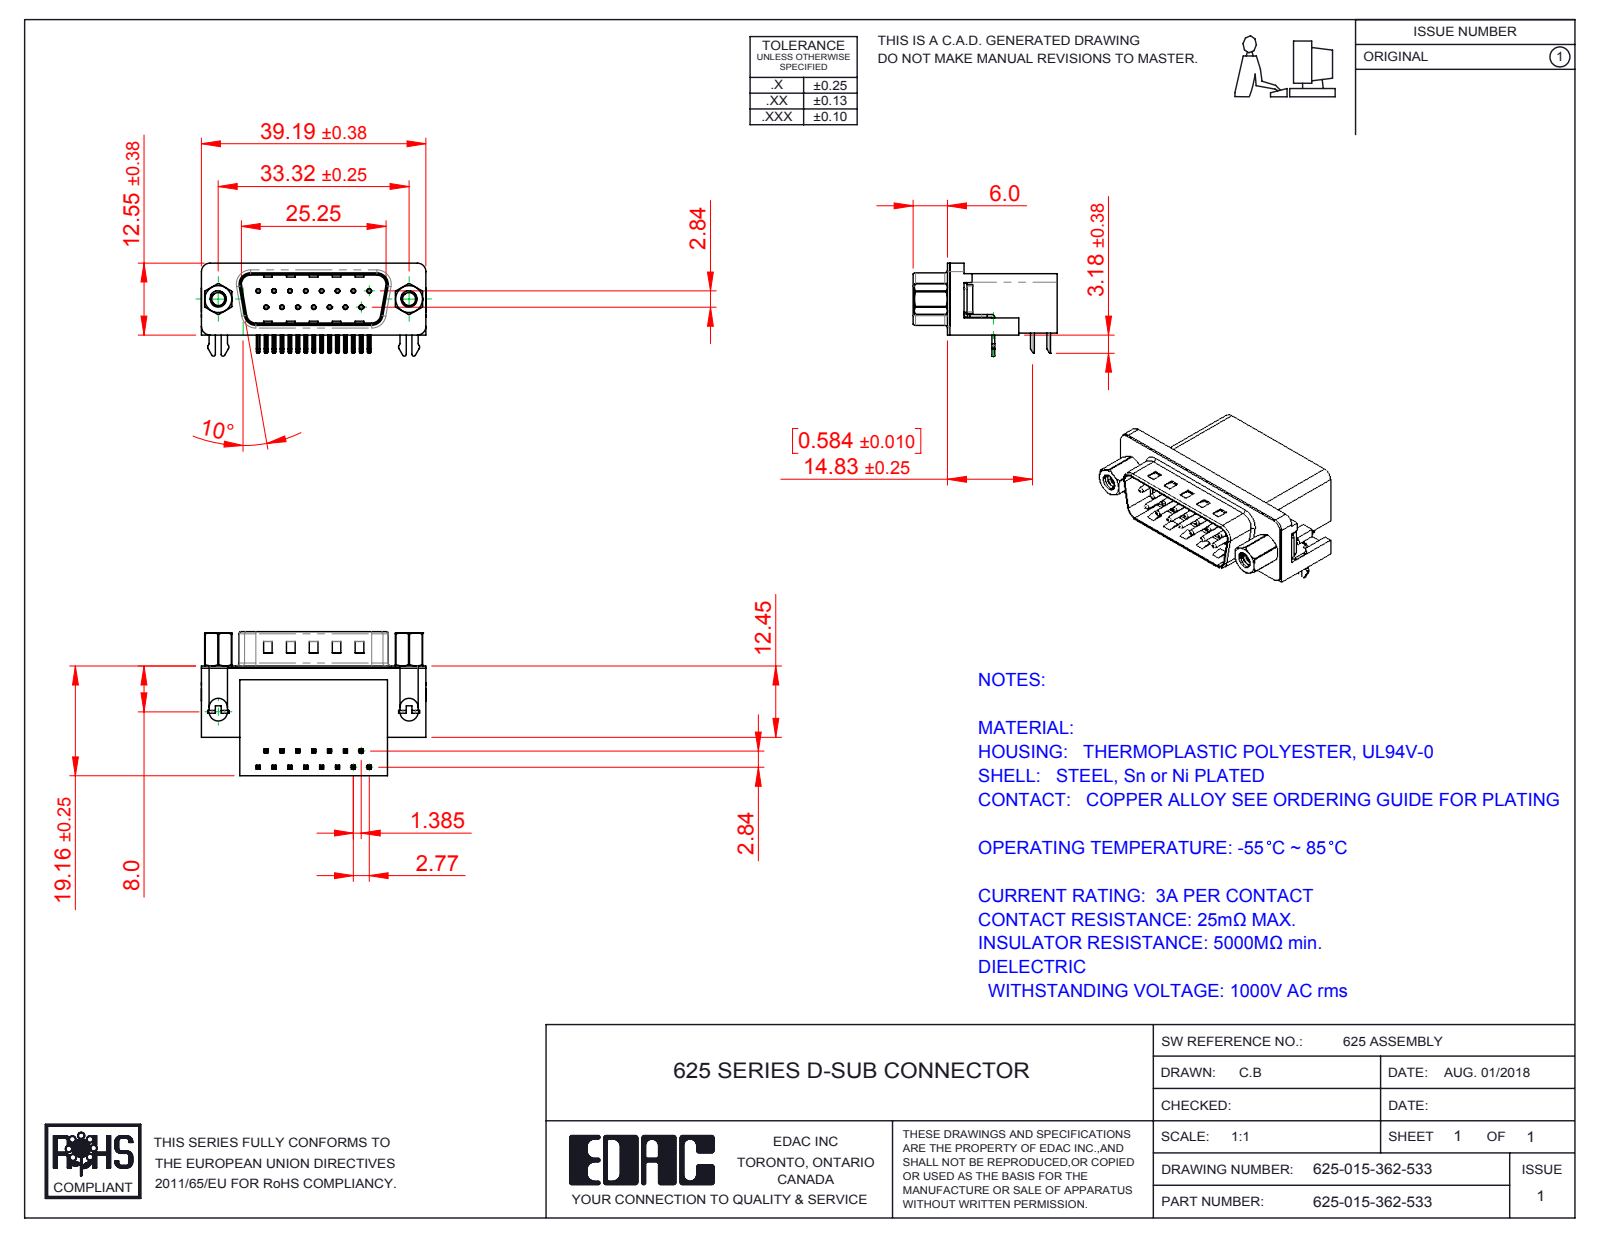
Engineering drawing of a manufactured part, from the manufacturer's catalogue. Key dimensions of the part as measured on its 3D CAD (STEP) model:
Part name (STEP PRODUCT): 625 Housing_15 Socket; 625 4-40 Hex Standoff 5; 625-015-362-533; 625 Contact Bottom (+4 more)
STEP written by: SolidWorks 2016 (CONFIG_CONTROL_DESIGN)
Units: millimetres
Bodies: 23 solids, 1645 faces (947 planar, 527 cylindrical, 171 other)
Overall size (bounding box): 39.22 × 25.16 × 16.25
Volume: 6 455 mm³ · Surface area: 6 913 mm²
Round holes (diameter × count): ⌀0.35 ×15, ⌀0.8 ×15, ⌀2.26 ×2, ⌀2.29 ×2, ⌀4 ×2, ⌀4.8 ×2, ⌀5 ×2
Round bosses / shafts (diameter × count): ⌀0.75 ×15, ⌀4.9 ×2, ⌀4.75 ×2, ⌀3.9 ×2, ⌀2.79 ×2
Partial cylindrical surfaces — rounded edges, fillets, slot ends (radius × count): R0.25 ×68, R0.12 ×30, R1 ×16, R0.5 ×14, R1.6 ×8, R1.5 ×6, R0.32 ×4, R0.9 ×4
Main face-to-face distances: 0.4, 10.35, 18.76, 2.1, 19.16, 10.46, 1.7, 10.86, 8.76, 16.26
Hole centre spacings: 3.16, 2.77, 5.54, 8.31, 11.08, 5.03, 5.04, 7.48
